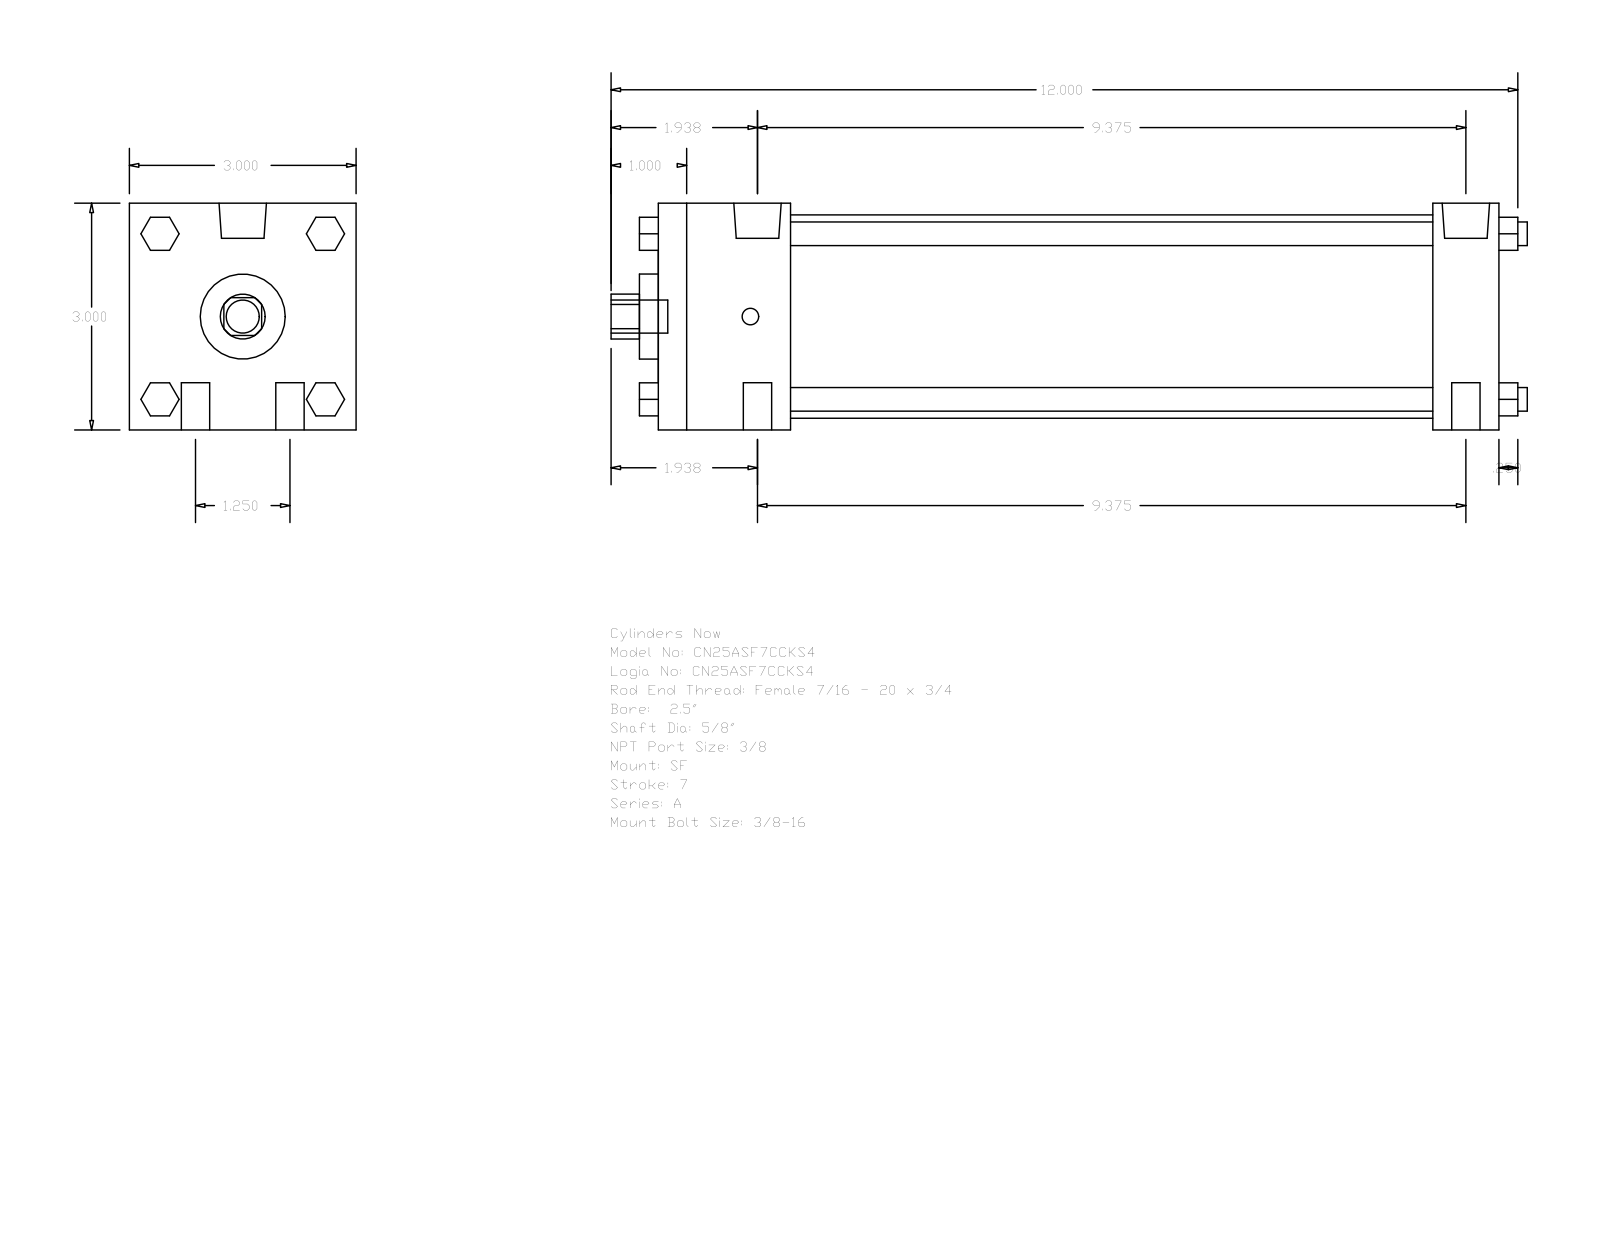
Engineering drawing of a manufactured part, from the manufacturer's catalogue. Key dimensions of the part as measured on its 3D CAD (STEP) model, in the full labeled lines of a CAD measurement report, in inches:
Part name (STEP PRODUCT): A_SF__0250_0.625
STEP written by: GSSL Pune (CONFIG_CONTROL_DESIGN)
Units: inches
Bodies: 0 solids, 124 faces (94 planar, 30 cylindrical, 0 other)
Overall size (bounding box): 12.125 × 3 × 3
Round holes (diameter × count): ⌀0.625 ×1, ⌀1.125 ×1, ⌀2.69 ×1
Round bosses / shafts (diameter × count): ⌀0.375 ×4, ⌀0.313 ×4, ⌀0.627 ×2, ⌀0.219 ×2, ⌀0.437 ×1
Partial cylindrical surfaces — rounded edges, fillets, slot ends (radius × count): R0.297 ×1
Main face-to-face distances: 3, 11.125, 1.75, 10.25, 0.875, 8.5, 9.375, 0.25, 11.375, 2
